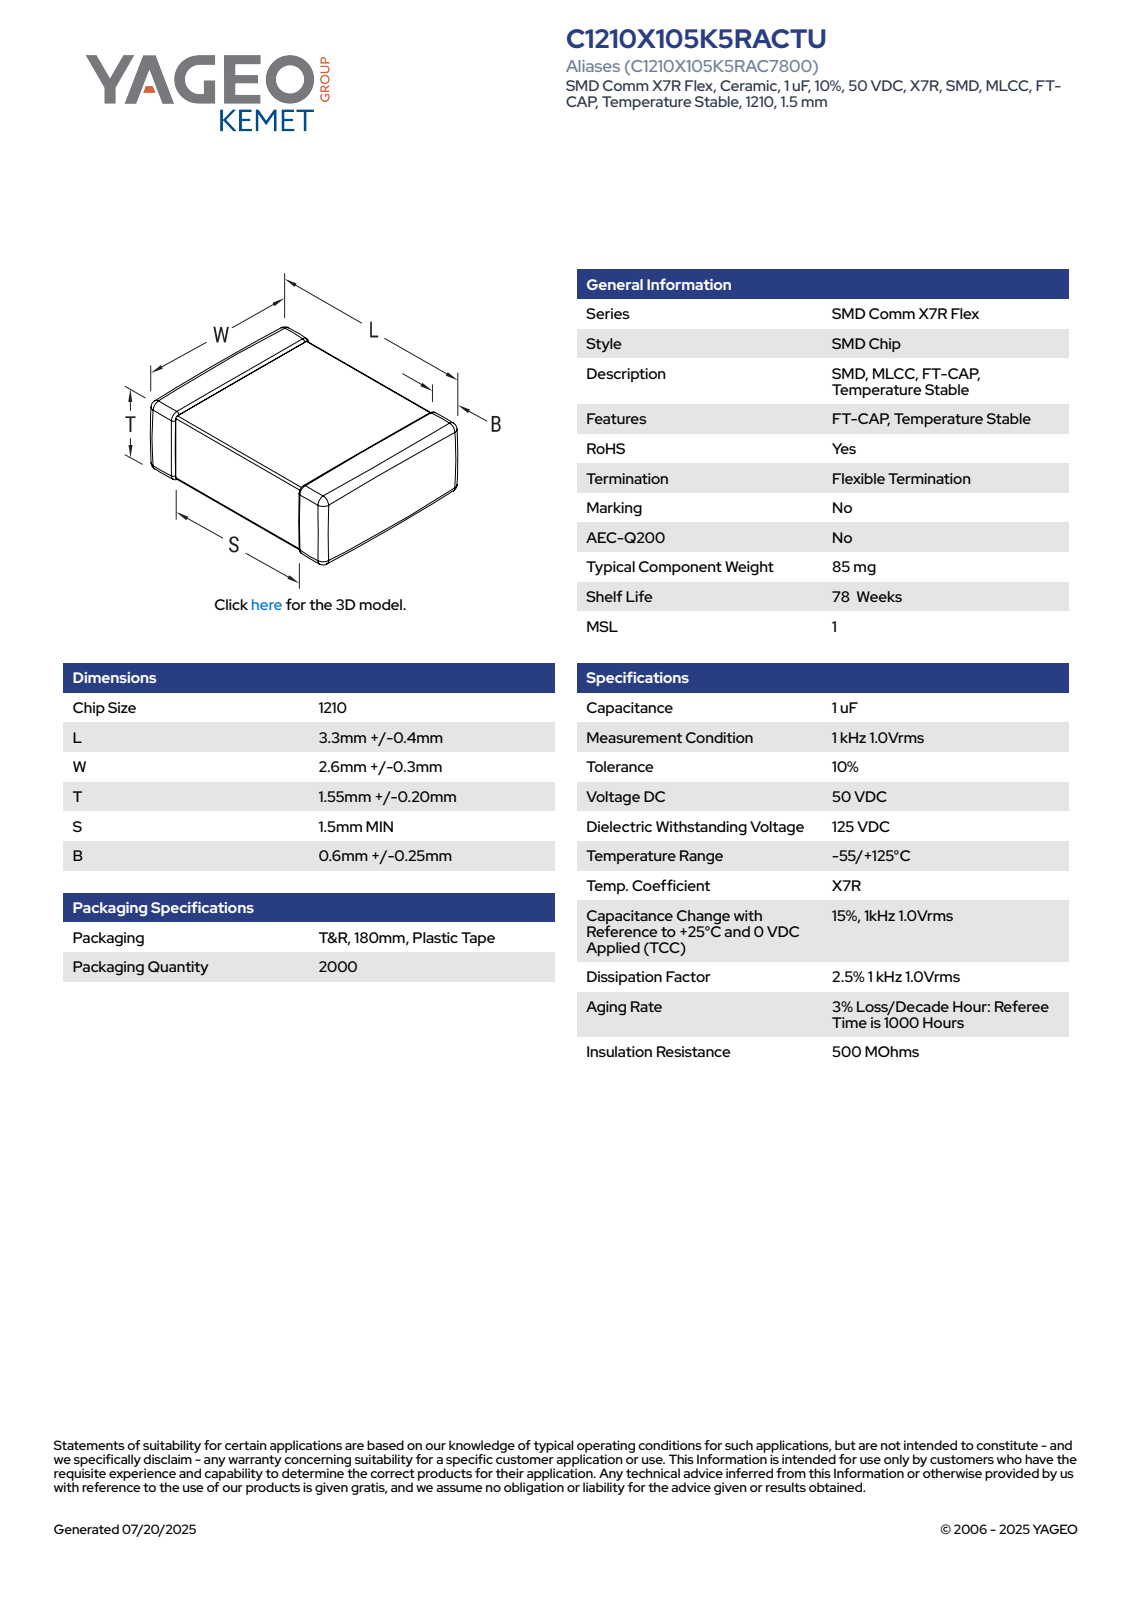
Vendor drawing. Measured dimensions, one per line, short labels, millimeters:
name: CCS_CCSTDNOS_1210_L3.7W2.9T1.75B0.85
written by: SolidWorks 2014 (AUTOMOTIVE_DESIGN)
unit: mm
bodies: 4 solids, 125 faces (71 planar, 38 cylindrical, 16 other)
size: 3.7 × 2.9 × 1.75
volume: 18 mm³; area: 44 mm²
face distances: 1.69, 1.63, 2.84, 3.7, 1.75, 2.78, 2.9, 1.4, 1.5, 1.34
